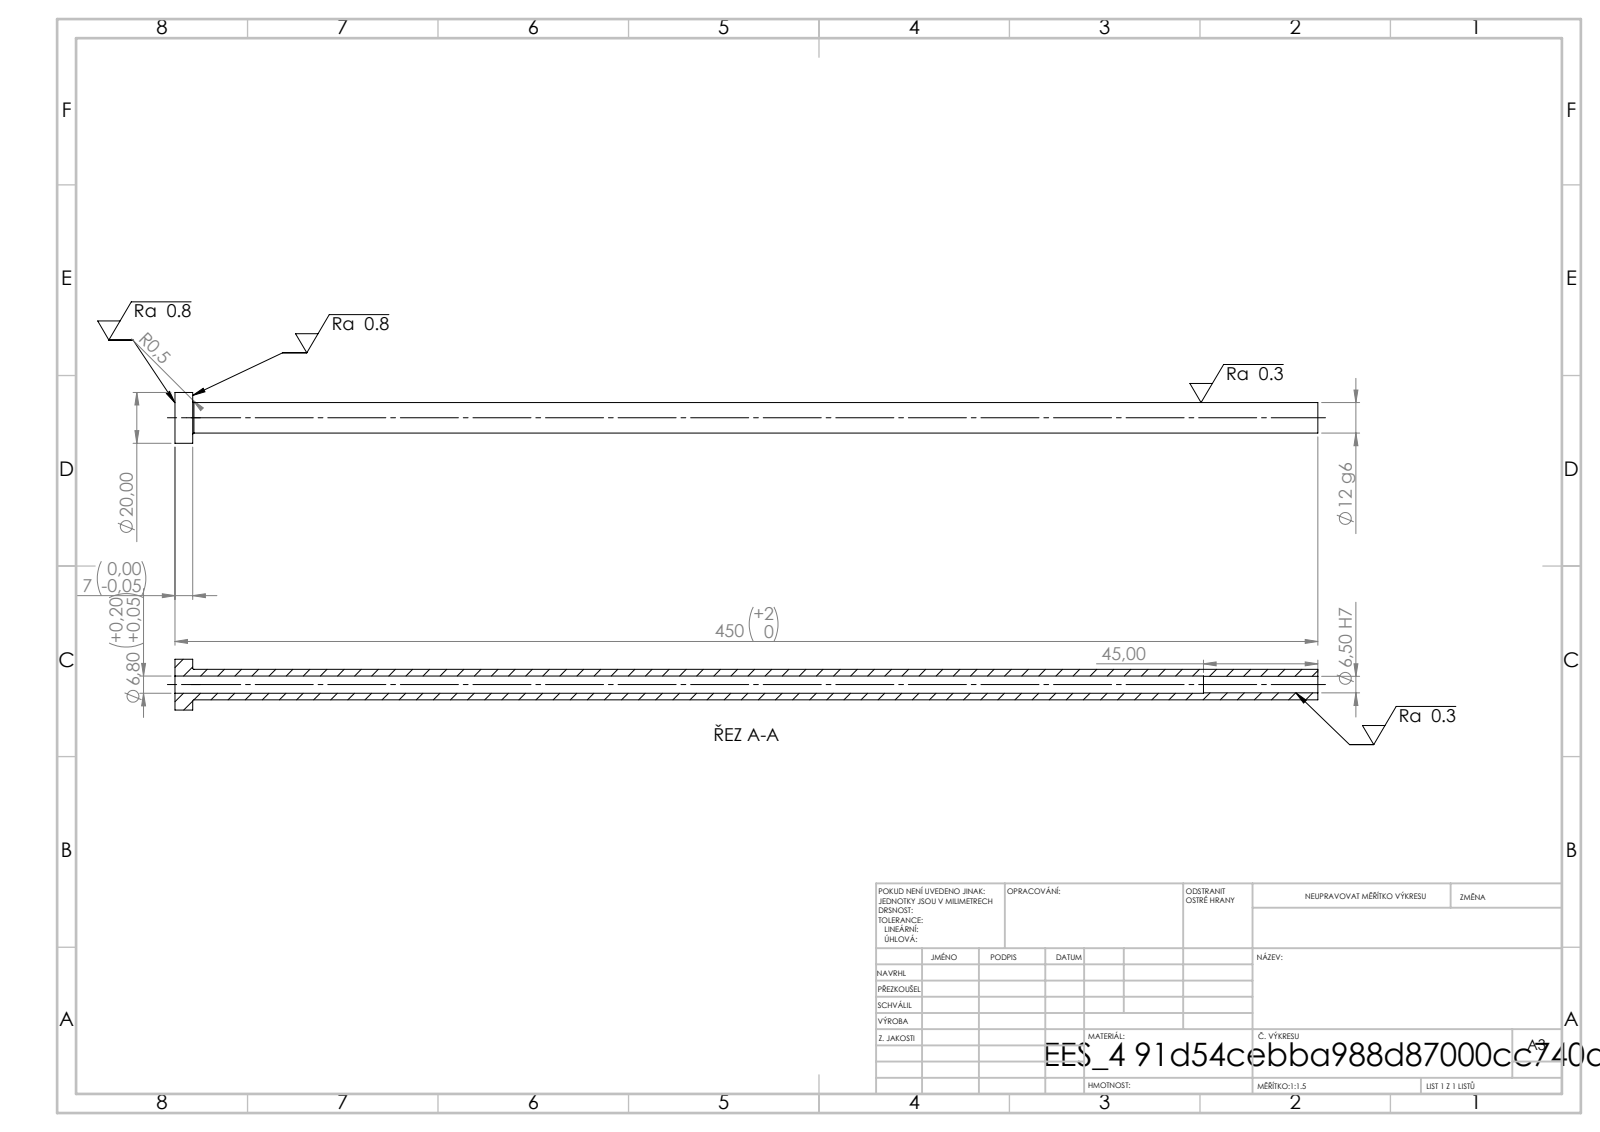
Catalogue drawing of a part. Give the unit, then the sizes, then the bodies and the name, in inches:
Units: inches
Overall size (bounding box): 17.717 × 0.787 × 0.787
Round holes (diameter × count): ⌀0.256 ×1, ⌀0.268 ×1
Round bosses / shafts (diameter × count): ⌀0.787 ×1, ⌀0.472 ×1
Main face-to-face distances: 0.276, 17.717, 17.441, 15.945, 15.669, 1.772
Volume: 2.203 in³ · Surface area: 42.26 in²
Bodies: 1 solid, 14 faces (4 planar, 8 cylindrical, 2 other)
STEP written by: SolidWorks 2019 (CONFIG_CONTROL_DESIGN)
